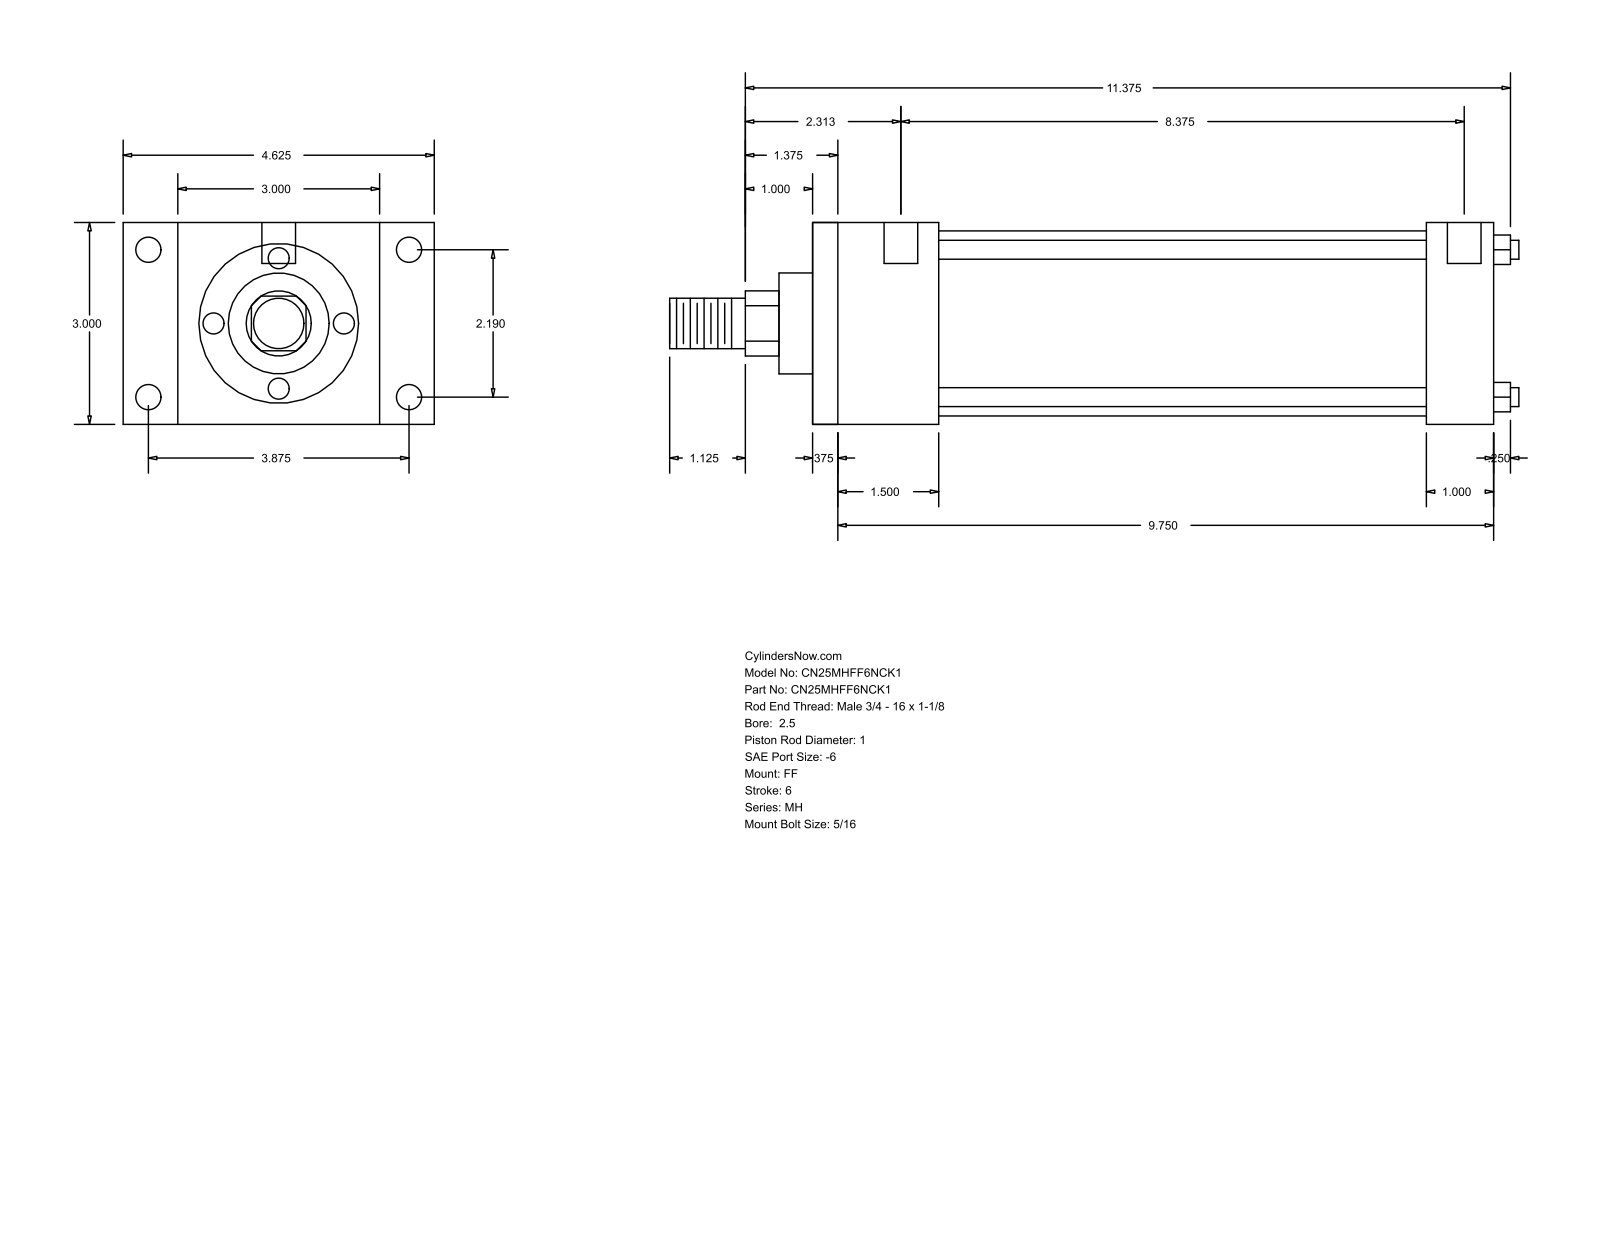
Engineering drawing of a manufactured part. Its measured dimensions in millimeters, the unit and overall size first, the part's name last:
Units: millimetres
Overall size (bounding box): 320.68 × 117.47 × 76.2
Round holes (diameter × count): ⌀5.56 ×4, ⌀9.53 ×4, ⌀12.7 ×2
Round bosses / shafts (diameter × count): ⌀7.14 ×4, ⌀69.85 ×1, ⌀38.1 ×1, ⌀25.4 ×1, ⌀19.05 ×1
Partial cylindrical surfaces — rounded edges, fillets, slot ends (radius × count): R12.29 ×1
Main face-to-face distances: 76.2, 257.17, 247.65, 9.52, 25.39, 47.63, 231.78, 38.11, 222.26, 184.15
Hole centre spacings: 55.62, 98.42, 113.05, 220.66, 3.18, 4.76, 212.72, 215.9
Bodies: 0 solids, 92 faces (64 planar, 28 cylindrical, 0 other)
Part name (STEP PRODUCT): MH_FF__0250_1
STEP written by: GSSL Pune (CONFIG_CONTROL_DESIGN)
